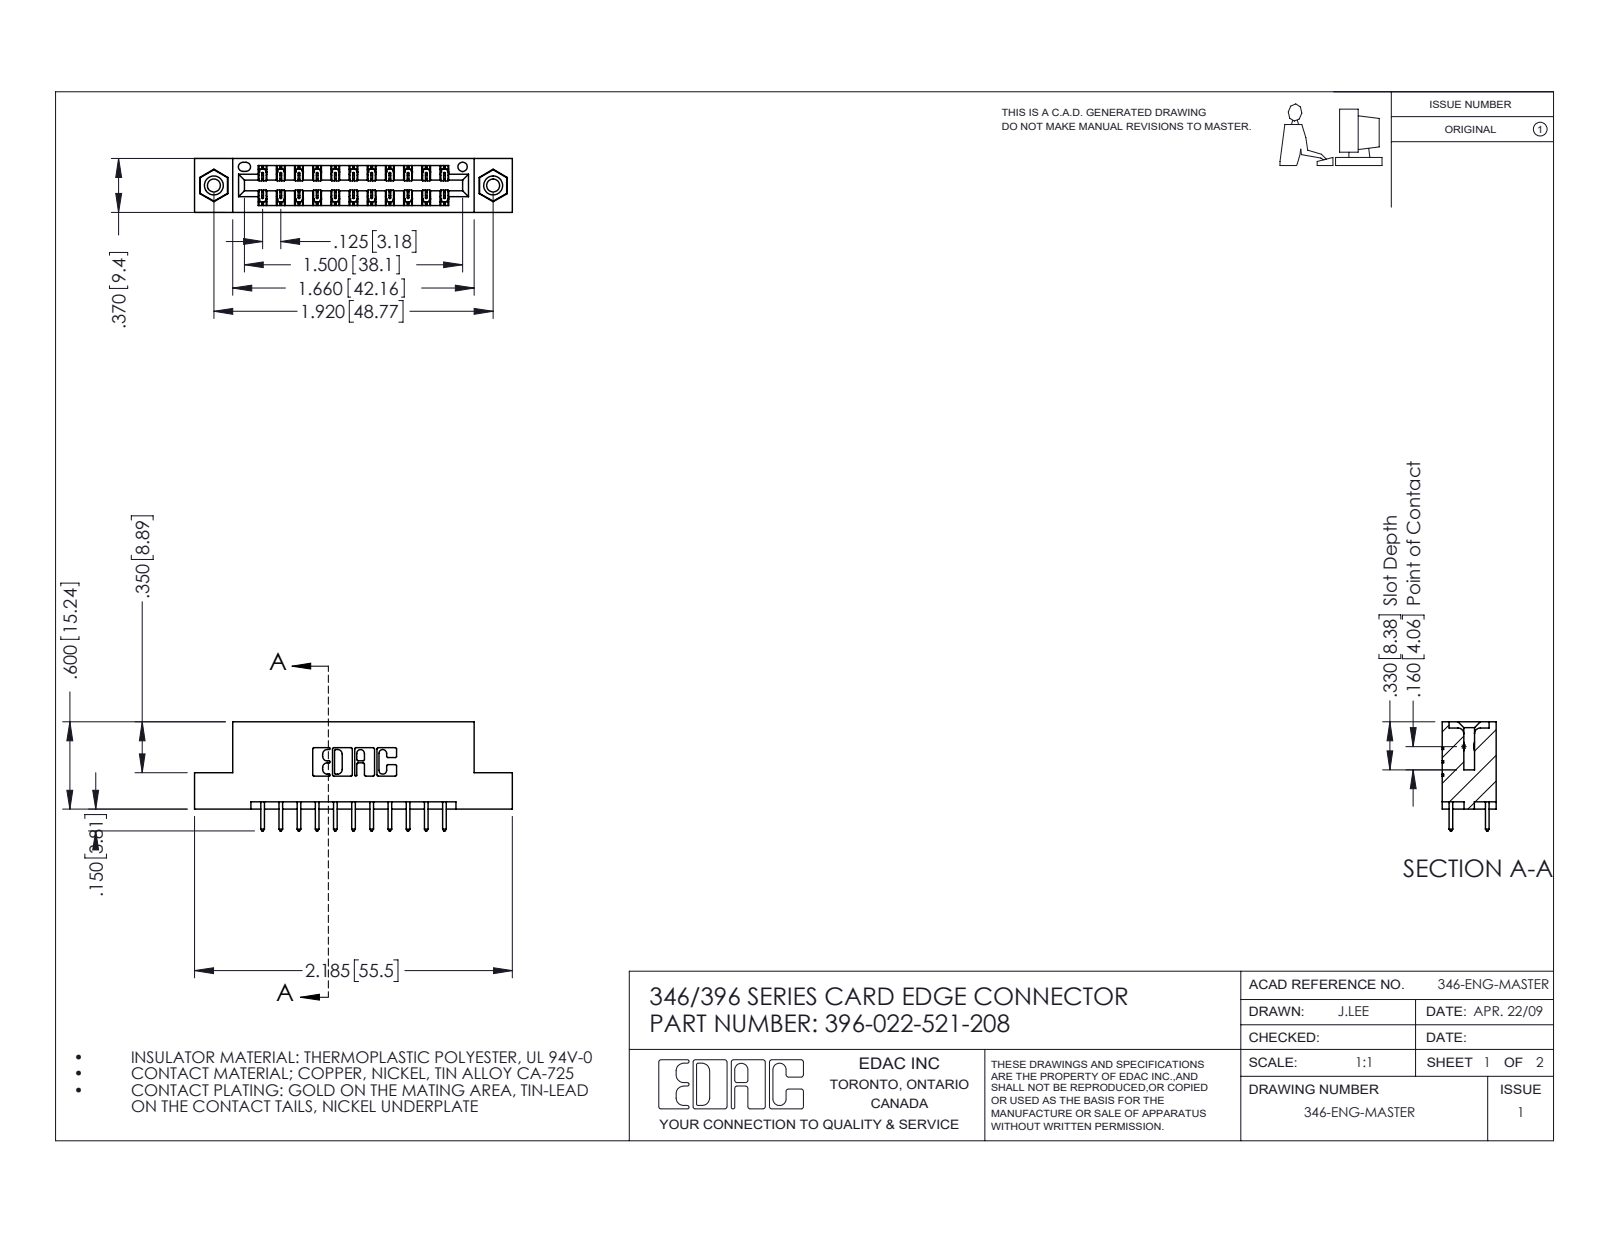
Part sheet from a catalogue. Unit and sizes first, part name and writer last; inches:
Units: inches
Overall size (bounding box): 2.185 × 0.75 × 0.37
Round holes (diameter × count): ⌀0.089 ×2, ⌀0.125 ×2, ⌀0.156 ×2, ⌀0.064 ×1
Round bosses / shafts (diameter × count): ⌀0.155 ×2
Partial cylindrical surfaces — rounded edges, fillets, slot ends (radius × count): R0.006 ×33, R0.01 ×22, R0.01 ×22, R0.007 ×6, R0.031 ×6, R0.026 ×3, R0.014 ×2, R0.022 ×2
Main face-to-face distances: 0.25, 0.048, 0.322, 0.37, 0.072, 0.298, 0.025, 0.275, 0.148, 0.222
Hole centre spacings: 0.246, 1.715, 1.92
Volume: 0.315 in³ · Surface area: 10.17 in²
Bodies: 25 solids, 1326 faces (878 planar, 432 cylindrical, 16 other)
Part name (STEP PRODUCT): 345-250-001_345-250-003-102; 346 Part_Flush Mounting Lugs - 0.156 Dia-TI; 345-292-001_345-293-121; 396-022-521-208
STEP written by: SolidWorks 2016 (CONFIG_CONTROL_DESIGN)
